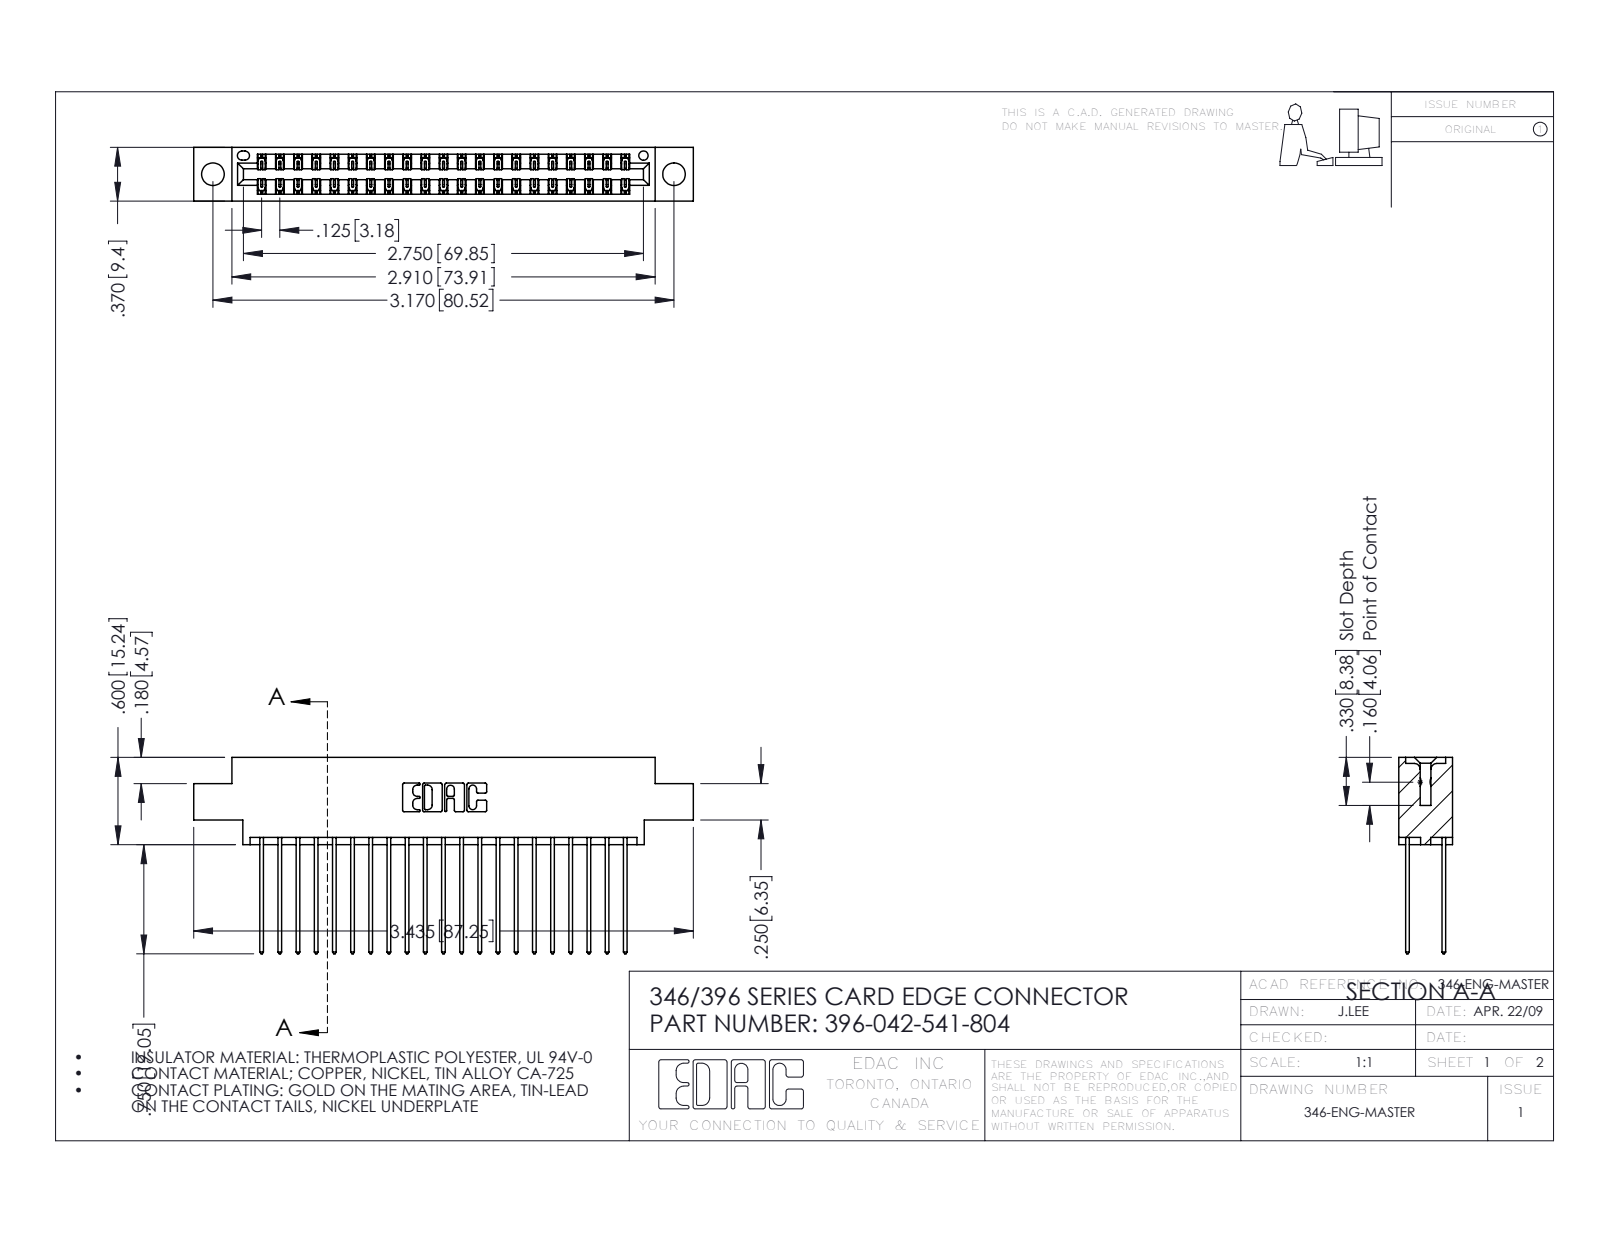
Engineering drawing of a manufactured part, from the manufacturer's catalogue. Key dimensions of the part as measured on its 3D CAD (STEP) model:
Part name (STEP PRODUCT): 396-042-541-804; 345-292-001_345-293-141; 346 Part_0.170 Offset - 0.156 Dia-TH
STEP written by: SolidWorks 2016 (CONFIG_CONTROL_DESIGN)
Units: inches
Bodies: 43 solids, 2310 faces (1550 planar, 760 cylindrical, 0 other)
Overall size (bounding box): 3.435 × 1.35 × 0.37
Volume: 0.509 in³ · Surface area: 19.04 in²
Round holes (diameter × count): ⌀0.156 ×2, ⌀0.064 ×1
Partial cylindrical surfaces — rounded edges, fillets, slot ends (radius × count): R0.006 ×63, R0.01 ×42, R0.01 ×22, R0.007 ×6, R0.031 ×6, R0.026 ×3, R0.014 ×2, R0.022 ×2
Main face-to-face distances: 0.048, 0.322, 0.25, 0.072, 0.298, 0.025, 0.37, 0.275, 0.225, 0.148
Hole centre spacings: 0.246, 2.963, 3.17
